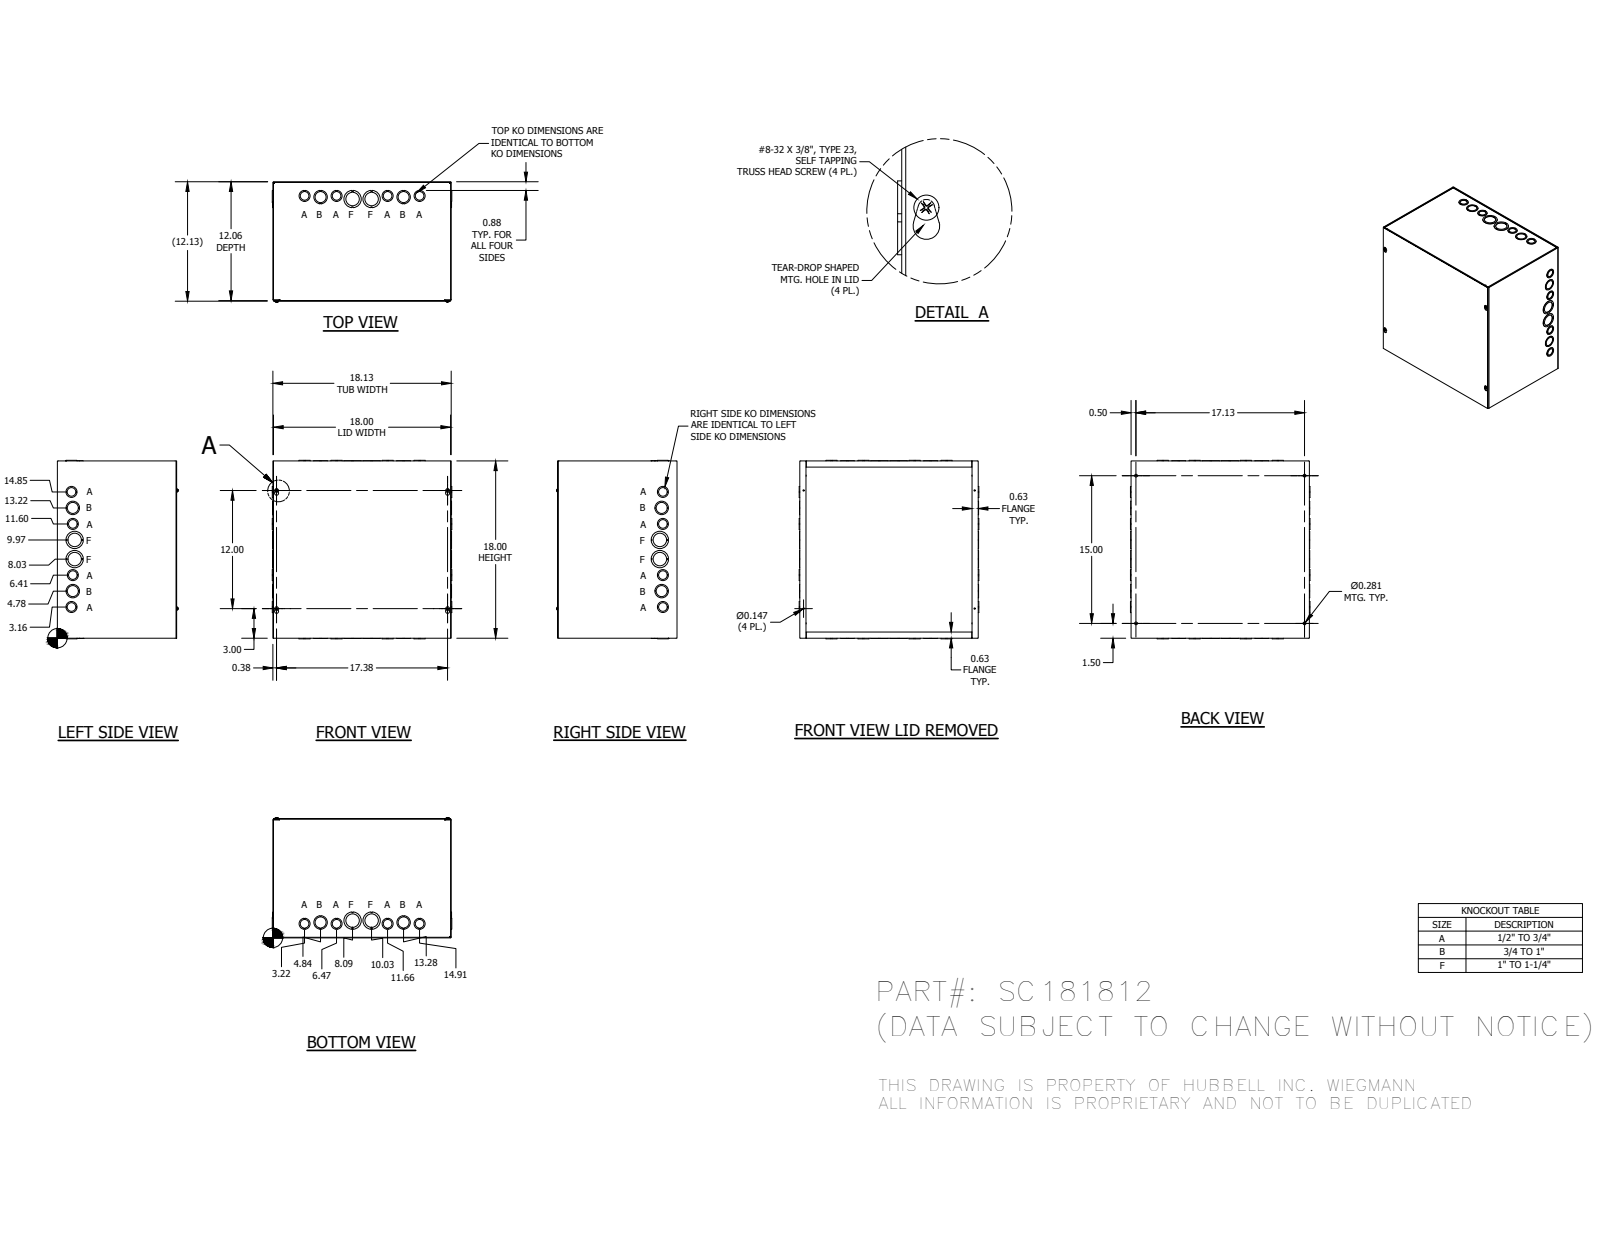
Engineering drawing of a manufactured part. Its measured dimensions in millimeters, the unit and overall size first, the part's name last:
Units: millimetres
Overall size (bounding box): 463.55 × 460.38 × 310.52
Round holes (diameter × count): ⌀28.57 ×14, ⌀22.22 ×10, ⌀34.92 ×8, ⌀3.73 ×4, ⌀7.14 ×4, ⌀44.45 ×4
Round bosses / shafts (diameter × count): ⌀9.75 ×4, ⌀4.17 ×4
Partial cylindrical surfaces — rounded edges, fillets, slot ends (radius × count): R0.79 ×12, R2.38 ×12, R3.17 ×4, R5.16 ×4
Main face-to-face distances: 1.59, 306.39, 457.2, 455.61, 458.79, 304.8, 307.98, 454.02, 460.38, 3.18
Hole centre spacings: 38.23, 41.39, 41.4, 42.03, 82.55, 82.69, 90.9, 124.07
Bodies: 37 solids, 1167 faces (859 planar, 240 cylindrical, 68 other)
Part name (STEP PRODUCT): SC181812BLR; SC1812TB; SC1818LPA; 34056 (+1 more)
STEP written by: Autodesk Inventor 2014 (AUTOMOTIVE_DESIGN)
